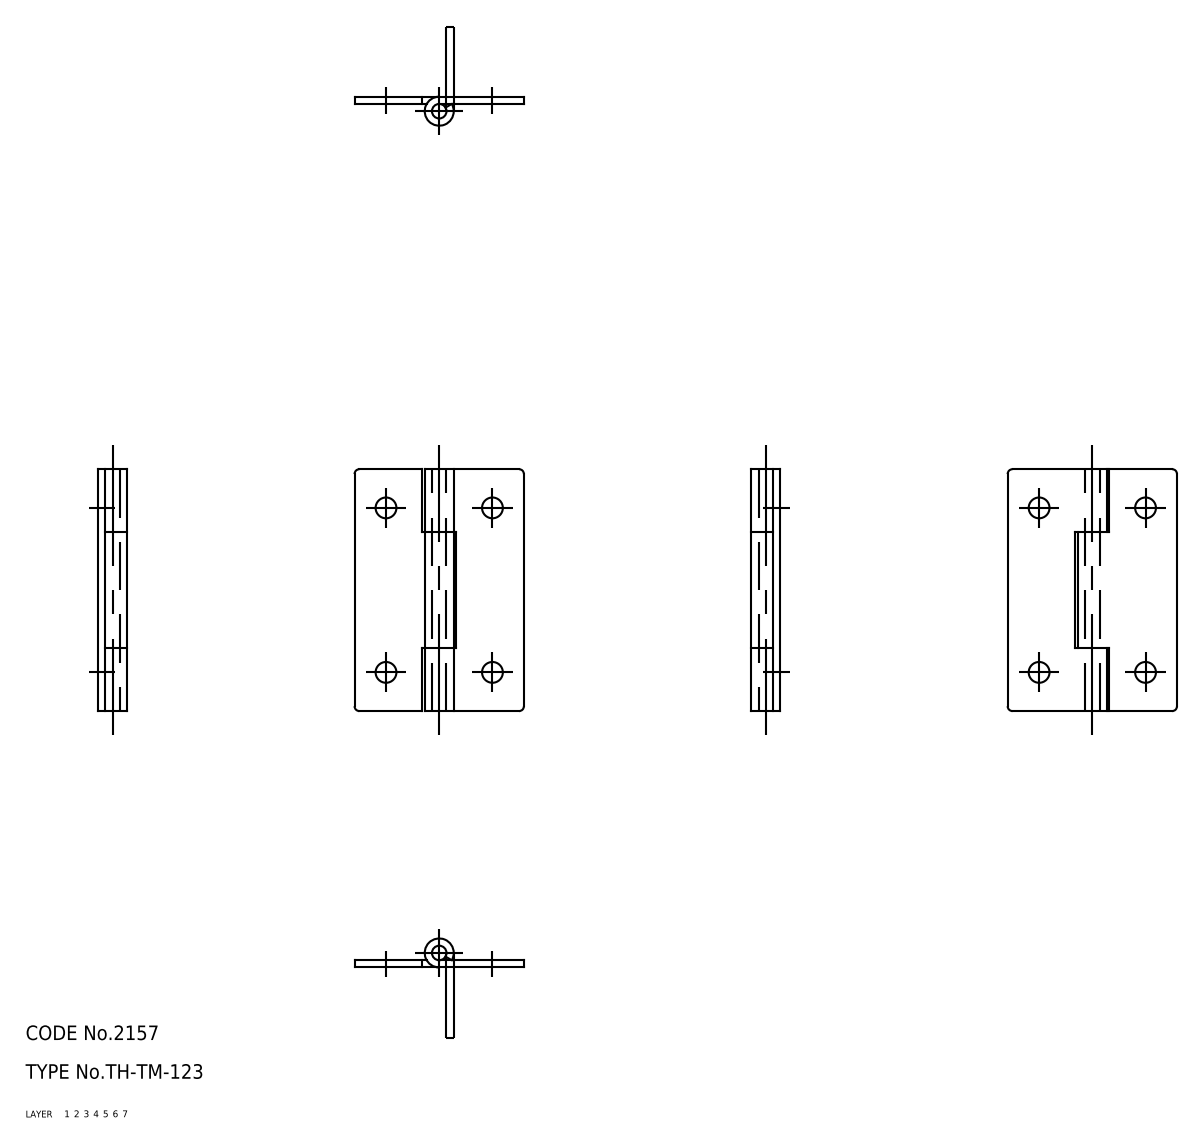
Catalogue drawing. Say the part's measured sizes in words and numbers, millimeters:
The part is named "hinge piece_B; hinge piece_A; shaft; TH_TM_123_21497_36". Its 3-D file was written by "CADfix (AUTOMOTIVE_DESIGN)". It is 3 solids with 42 faces: 0 planar, 0 cylindrical and 42 other. Overall it measures 50 by 35 by 6 millimeters. Its volume is 3 508 cubic millimeters and its surface area 5 292 square millimeters.
